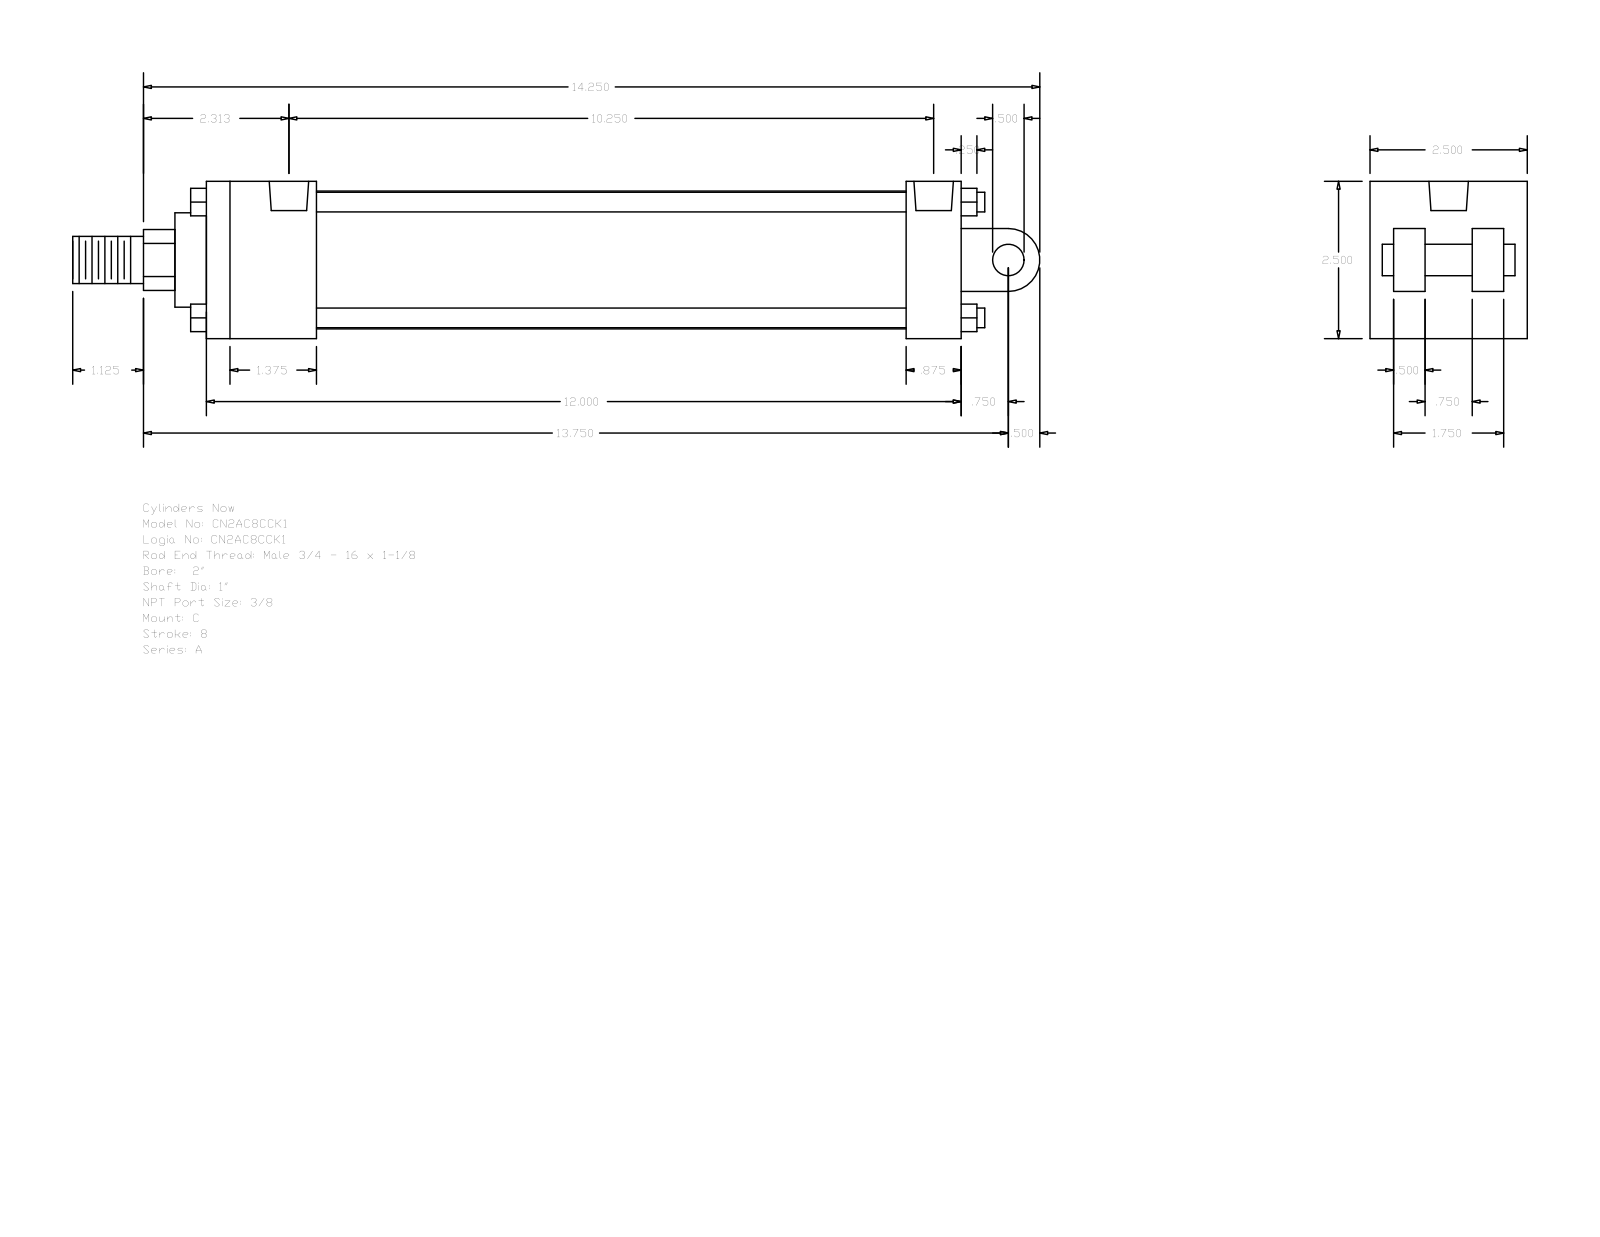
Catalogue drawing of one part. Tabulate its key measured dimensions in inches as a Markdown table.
| quantity | value |
| --- | --- |
| part name | A_C__0200_1 |
| STEP written by | GSSL Pune (CONFIG_CONTROL_DESIGN) |
| units | inches |
| bodies | 0 solids, 135 faces (102 planar, 33 cylindrical, 0 other) |
| overall size | 15.375 × 2.5 × 2.5 |
| round holes (diameter × count) | 0.219 × 4, 0.627 × 2 |
| round bosses / shafts (diameter × count) | 0.313 × 4, 2.19 × 1, 1.5 × 1, 1 × 1, 0.75 × 1, 0.5 × 1 |
| partial cylindrical surfaces (radius × count) | 0.484 × 1, 0.5 × 1 |
| main face-to-face distances | 2.5, 0.875, 12, 1.75, 0.5, 10.25, 11.125, 9.375, 0.375, 1.625 |
| hole center spacings | 10.031, 0.063, 0.157, 10.093, 10.187, 10.25 |
